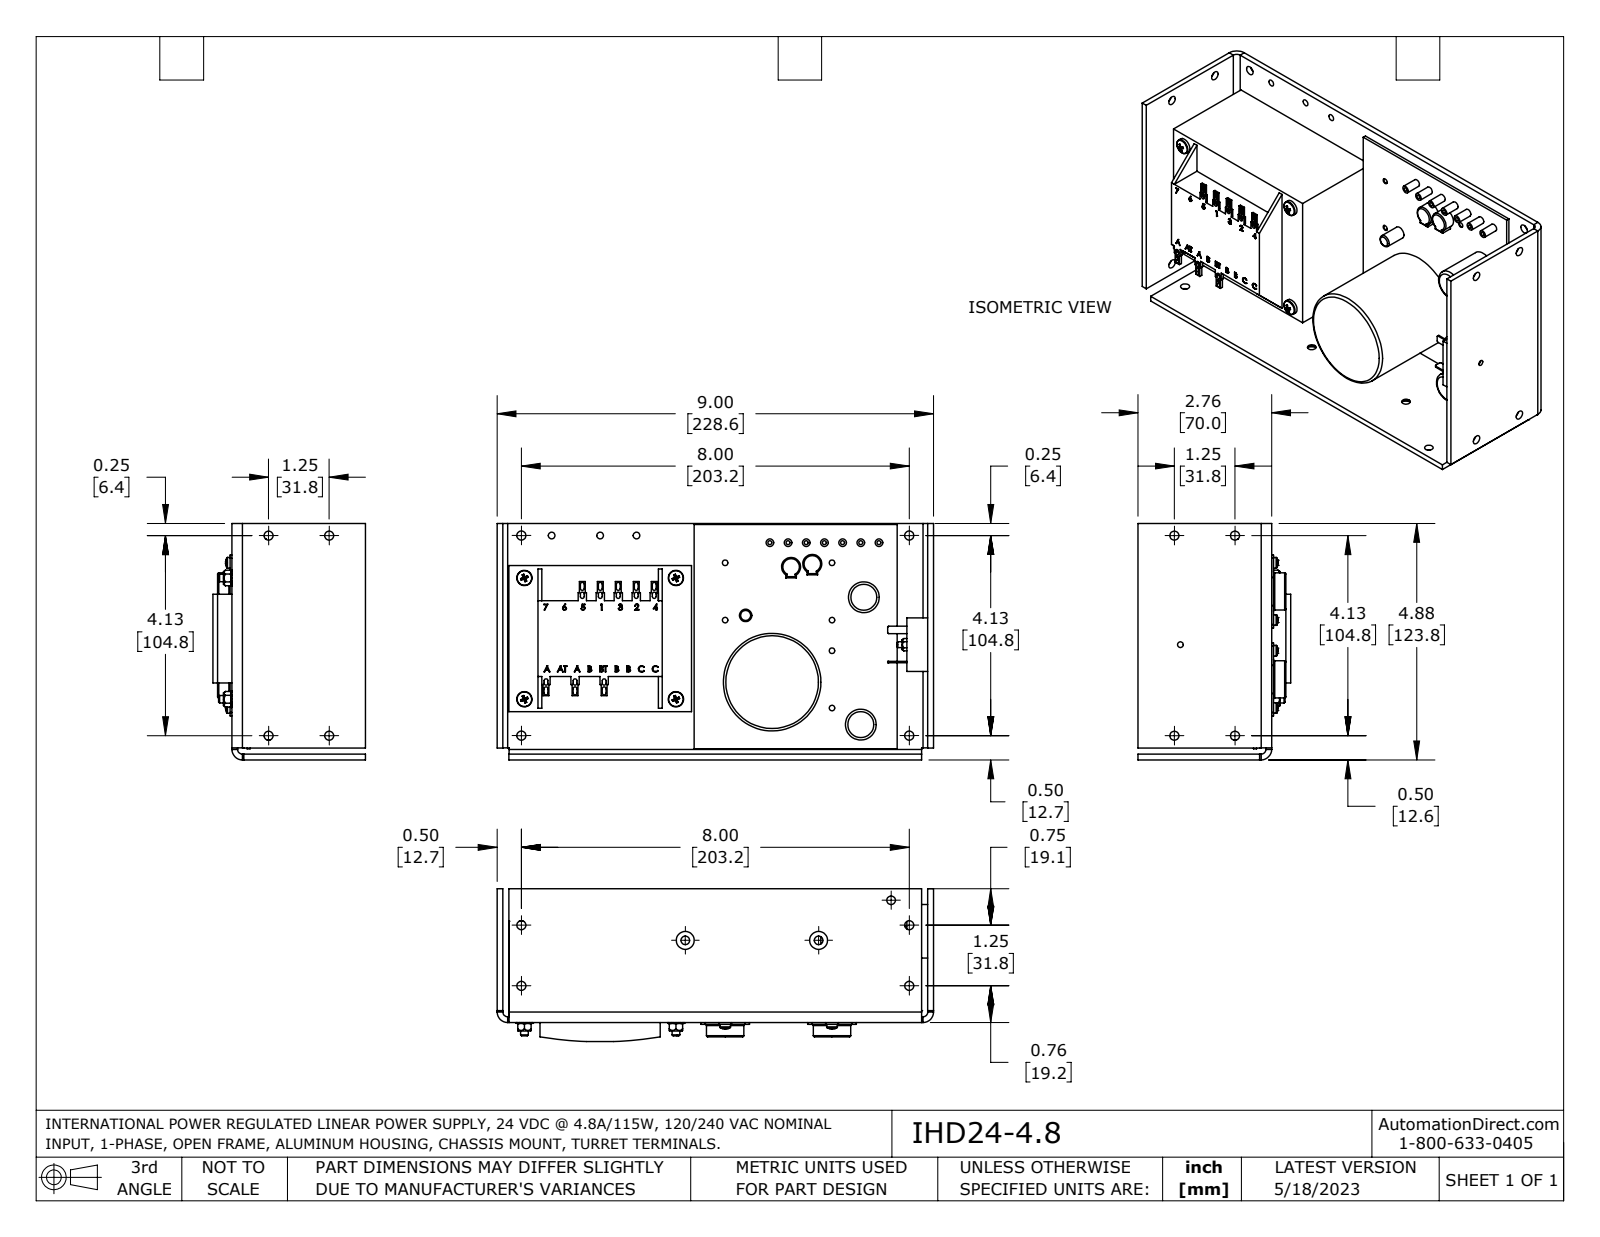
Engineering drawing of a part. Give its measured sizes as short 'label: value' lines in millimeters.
name: IHD24-4.8
written by: SolidWorks 2021 (AUTOMOTIVE_DESIGN)
unit: mm
bodies: 31 solids, 1344 faces (809 planar, 338 cylindrical, 197 other)
size: 228.6 × 123.8 × 80
volume: 764 900 mm³; area: 210 600 mm²
holes: 12× ⌀4.7, 7× ⌀2, 6× ⌀2.9, 6× ⌀4, 6× ⌀5, 5× ⌀3.3, 4× ⌀4.3, 3× ⌀3.5, 3× ⌀4.5, 2× ⌀4, 2× ⌀12.7, 1× ⌀2.5
bosses: 9× ⌀4, 6× ⌀6, 6× ⌀5.6, 6× ⌀3, 4× ⌀8, 3× ⌀19.5, 2× ⌀16.2, 2× ⌀10
rounds: 32× R1, 6× R0.6, 6× R4.1, 4× R3.2, 4× R4.2, 3× R2.5, 3× R5.5, 3× R12.8
face distances: 3, 225.6, 4.9, 7.9, 6.5, 1.6, 9.5, 222.6, 228.6, 53
hole spacings: 63.5, 9.4, 31.8, 104.8, 203.2, 0.8, 10, 15.9
